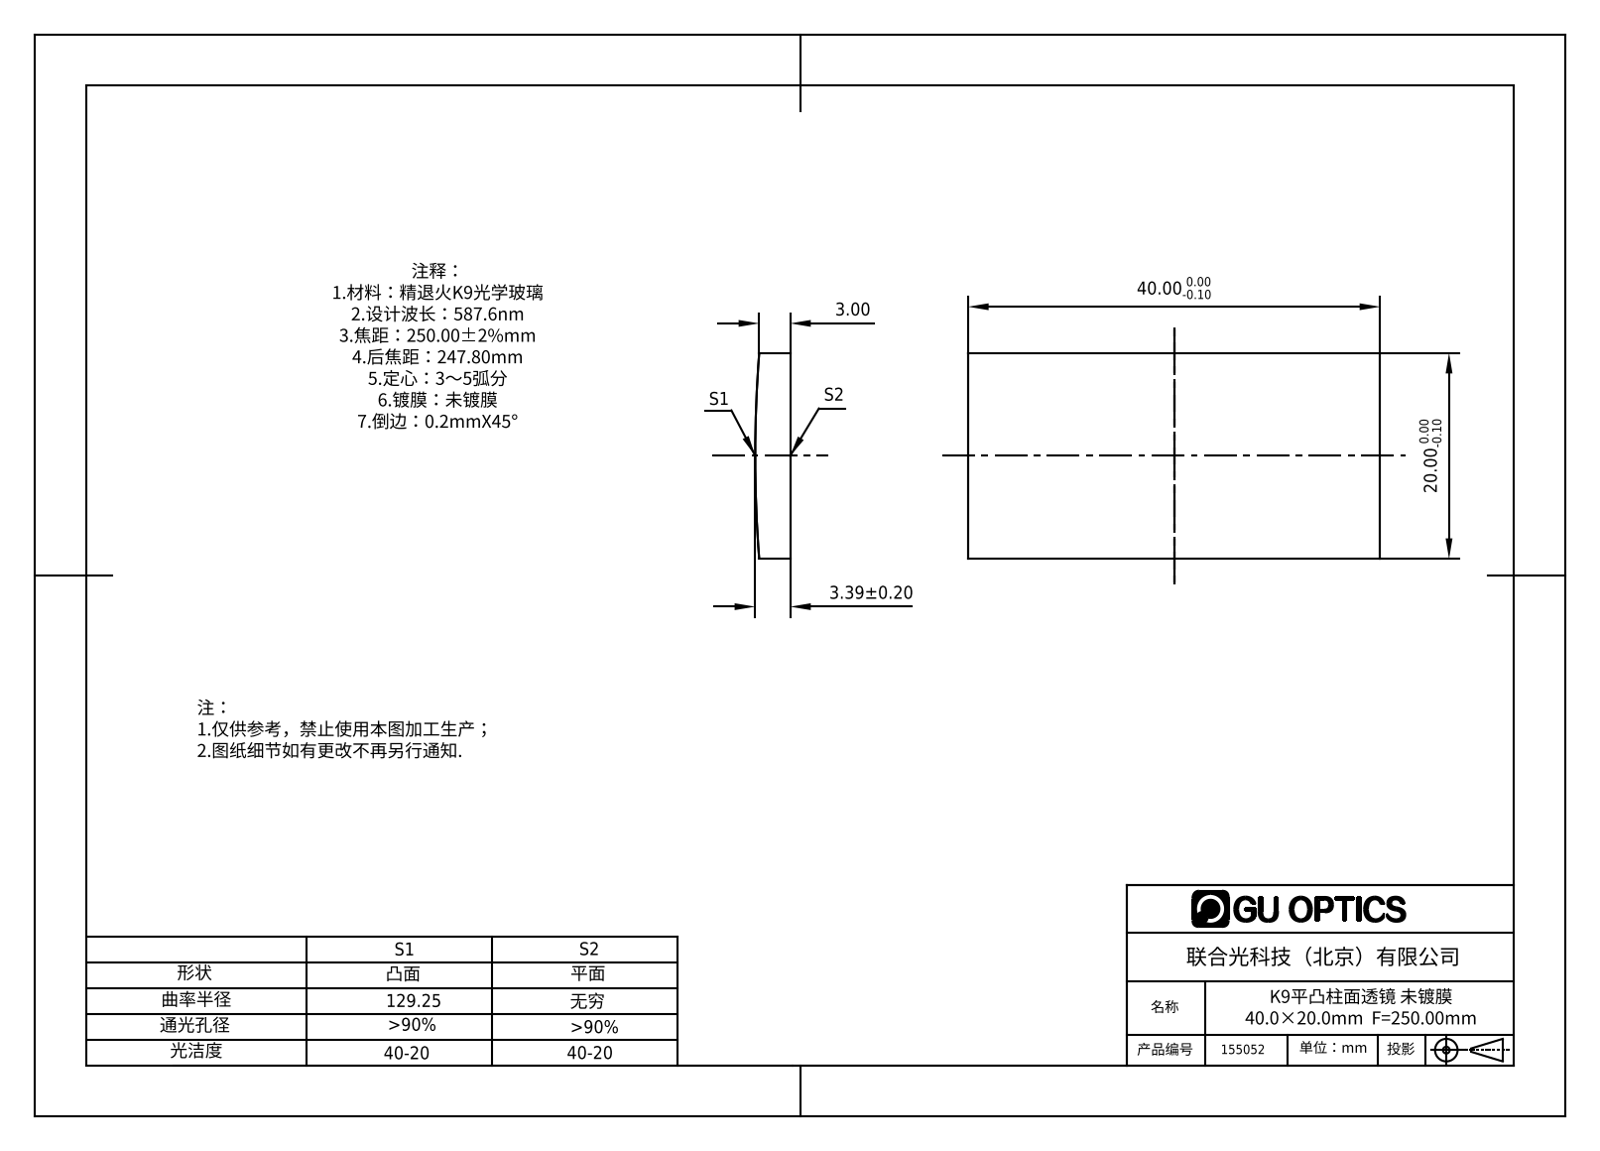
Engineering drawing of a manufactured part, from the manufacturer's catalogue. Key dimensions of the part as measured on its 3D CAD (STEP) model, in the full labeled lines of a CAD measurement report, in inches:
Part name (STEP PRODUCT): 155052
STEP written by: SolidWorks 2016 (AUTOMOTIVE_DESIGN)
Units: inches
Bodies: 1 solid, 6 faces (5 planar, 1 cylindrical, 0 other)
Overall size (bounding box): 1.575 × 0.787 × 0.133
Volume: 0.159 in³ · Surface area: 3.055 in²
Partial cylindrical surfaces — rounded edges, fillets, slot ends (radius × count): R5.089 ×1
Main face-to-face distances: 0.787, 1.575
